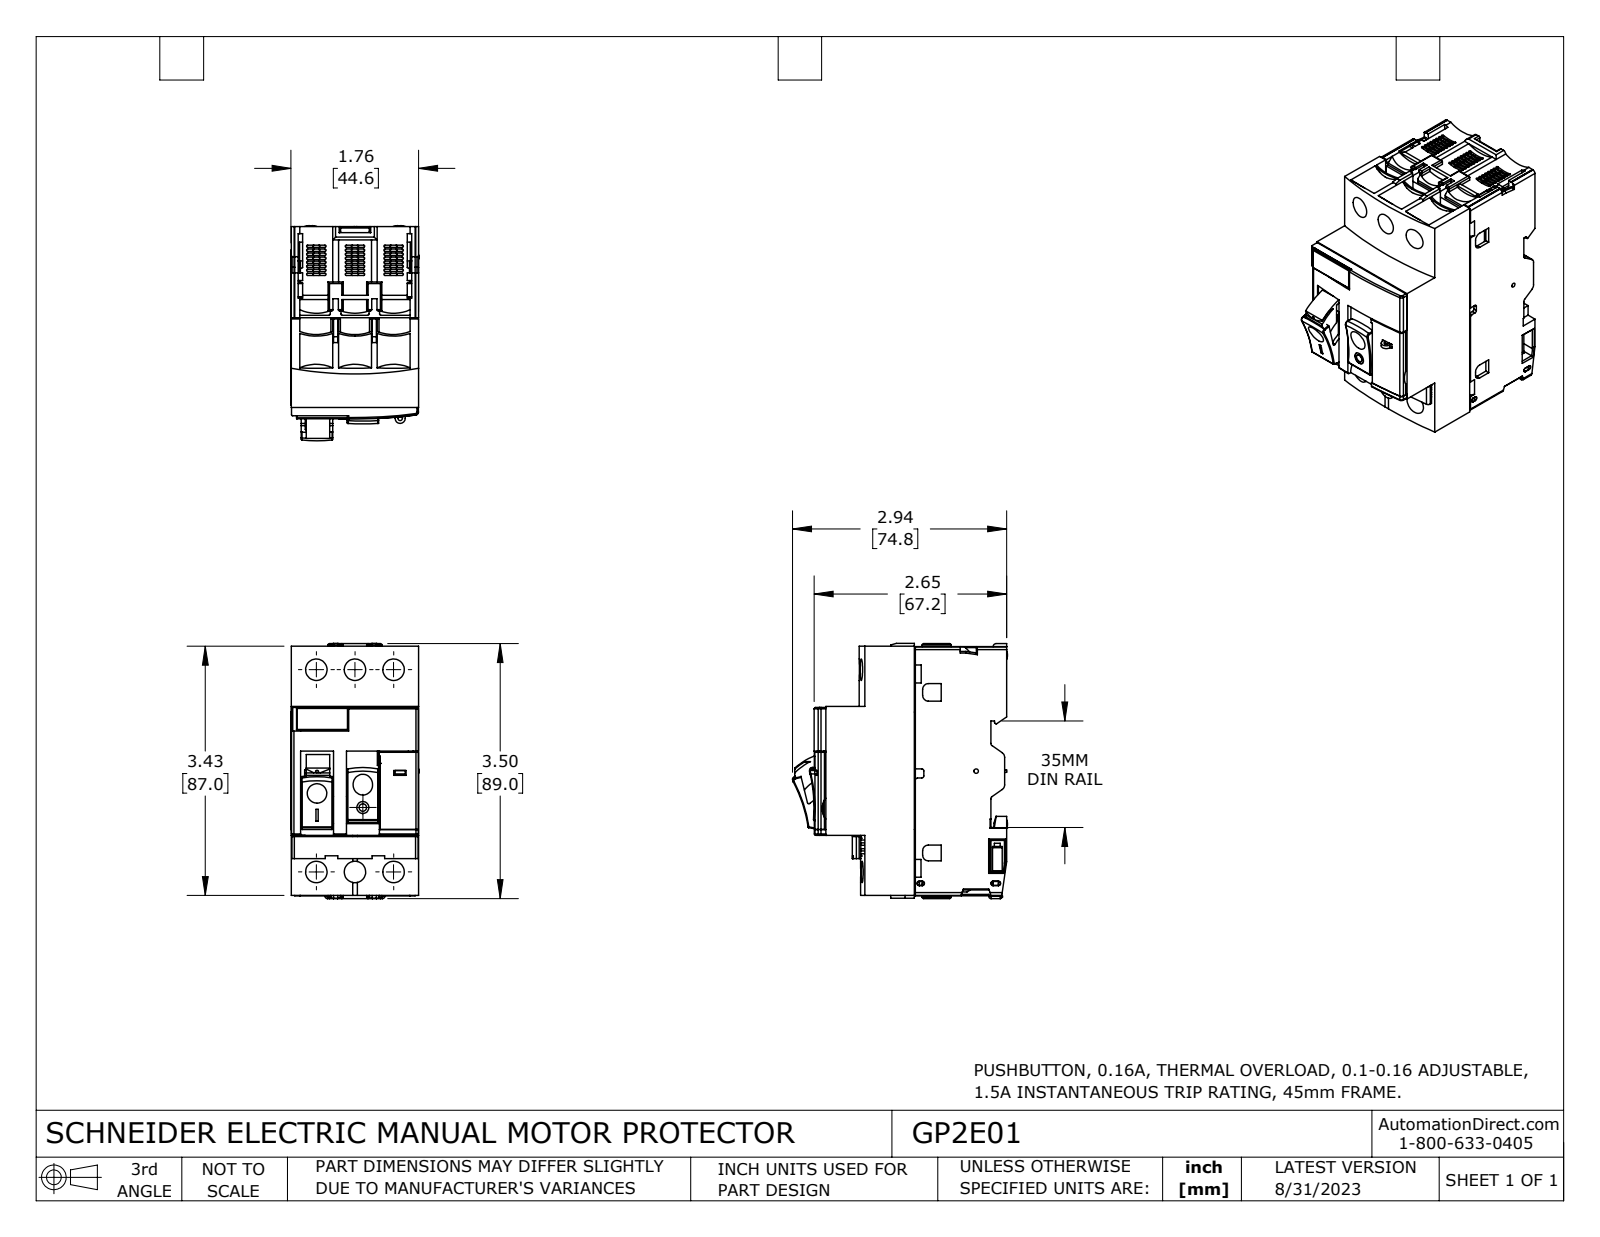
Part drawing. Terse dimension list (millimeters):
name: GP2E01
written by: SolidWorks 2021 (CONFIG_CONTROL_DESIGN)
unit: mm
bodies: 15 solids, 2269 faces (1521 planar, 657 cylindrical, 91 other)
size: 89.1 × 75.1 × 44.8
volume: 189 800 mm³; area: 63 830 mm²
holes: 6× ⌀7.5, 5× ⌀5, 2× ⌀1.5, 1× ⌀4, 1× ⌀4.2, 1× ⌀8, 1× ⌀8.3, 1× ⌀8.5, 1× ⌀8.7
bosses: 2× ⌀6.2, 2× ⌀3, 1× ⌀9.7, 1× ⌀2.6, 1× ⌀1.2
rounds: 104× R0.4, 47× R0.5, 16× R1, 12× R0.3, 12× R0.3, 12× R0.8, 8× R1.5, 6× R0.1
face distances: 44.5, 13.5, 2.9, 31.3, 44.6, 1.5, 41.6, 14.8, 26.7, 29.7
hole spacings: 13.5, 71.9, 70.6, 8.8, 10.2, 13.9, 17, 18.4
